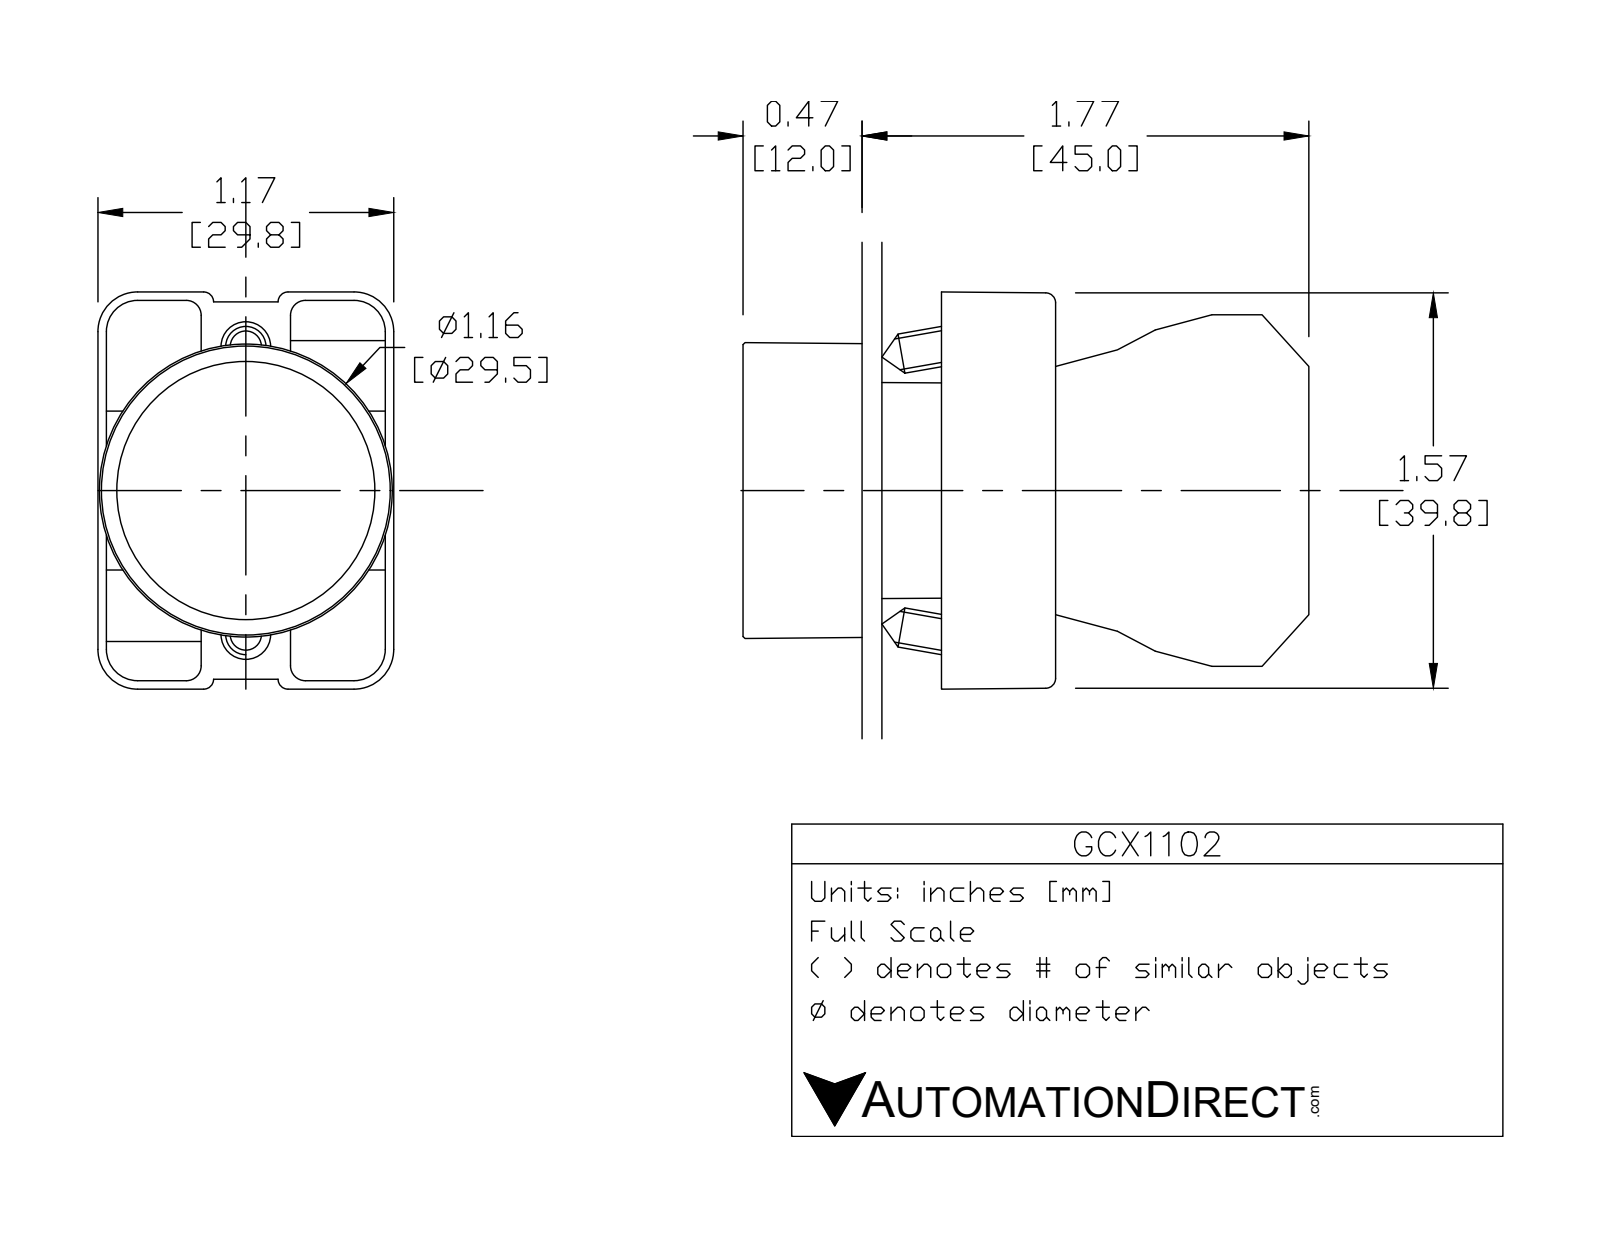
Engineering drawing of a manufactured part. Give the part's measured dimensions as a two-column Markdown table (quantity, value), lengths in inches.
| quantity | value |
| --- | --- |
| part name | GCX1102; ecx1029; ecx1040; GCX1102 OPERATOR |
| STEP written by | SolidWorks 2016 (AUTOMOTIVE_DESIGN) |
| units | inches |
| bodies | 6 solids, 381 faces (222 planar, 132 cylindrical, 27 other) |
| overall size | 2.217 × 1.581 × 1.177 |
| volume | 1.741 in³ |
| surface area | 27.14 in² |
| round holes (diameter × count) | 0.079 × 2, 0.124 × 2, 0.13 × 2, 0.087 × 1, 0.197 × 1, 0.878 × 1, 0.888 × 1, 1.024 × 1 |
| round bosses / shafts (diameter × count) | 0.157 × 2, 1.175 × 1, 1.004 × 1, 0.945 × 1, 0.856 × 1, 0.78 × 1 |
| partial cylindrical surfaces (radius × count) | 0.059 × 24, 0.041 × 12, 0.124 × 12, 0.157 × 12, 0.039 × 4, 0.128 × 2, 0.02 × 1, 0.063 × 1 |
| main face-to-face distances | 0.72, 0.579, 0.033, 0.472, 1.193, 0.031, 0.689, 0.598, 1.161, 1.071 |
| hole center spacings | 0.236, 0.544, 0.472, 0.49 |
